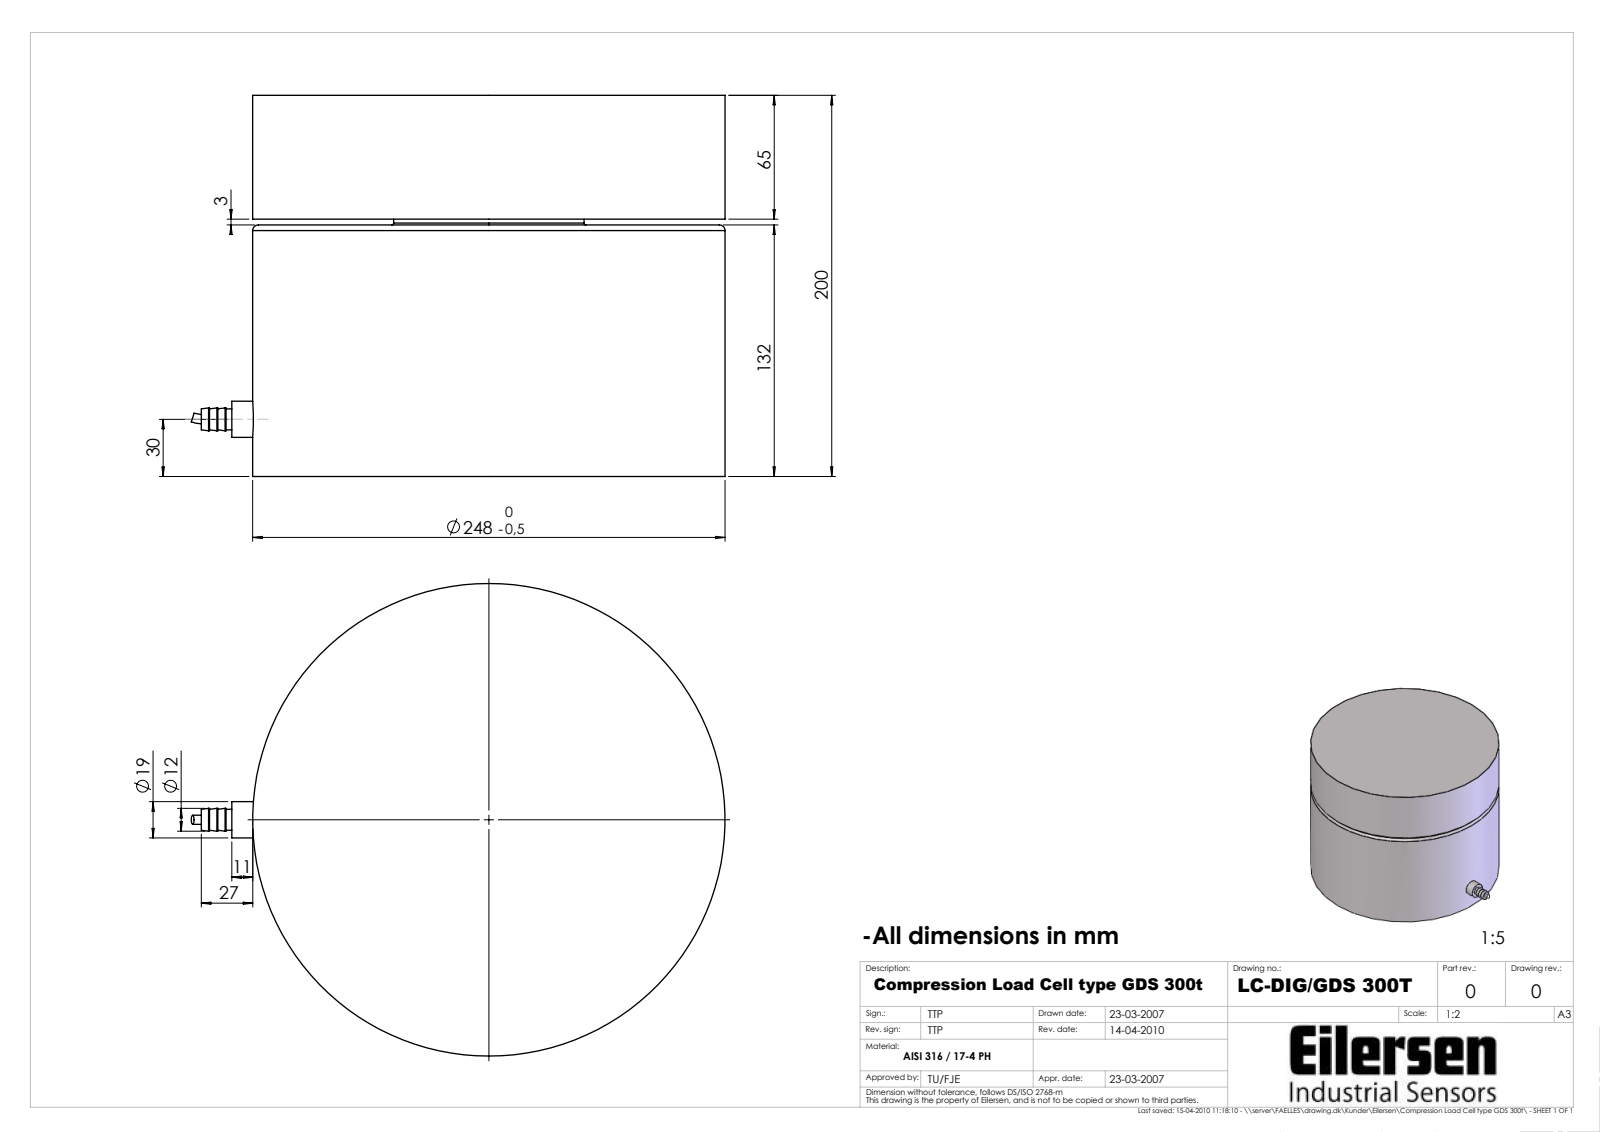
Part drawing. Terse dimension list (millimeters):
name: Compression Load Cell type GDS 300t
written by: SolidWorks 2009 (CONFIG_CONTROL_DESIGN)
unit: mm
bodies: 2 solids, 44 faces (12 planar, 18 cylindrical, 14 other)
size: 280.25 × 248 × 200
volume: 9 543 000 mm³; area: 357 165 mm²
holes: 1× ⌀100
bosses: 1× ⌀248, 1× ⌀19, 1× ⌀12, 1× ⌀11
face distances: 200, 135, 65, 3, 132, 68, 150, 18, 15, 50
